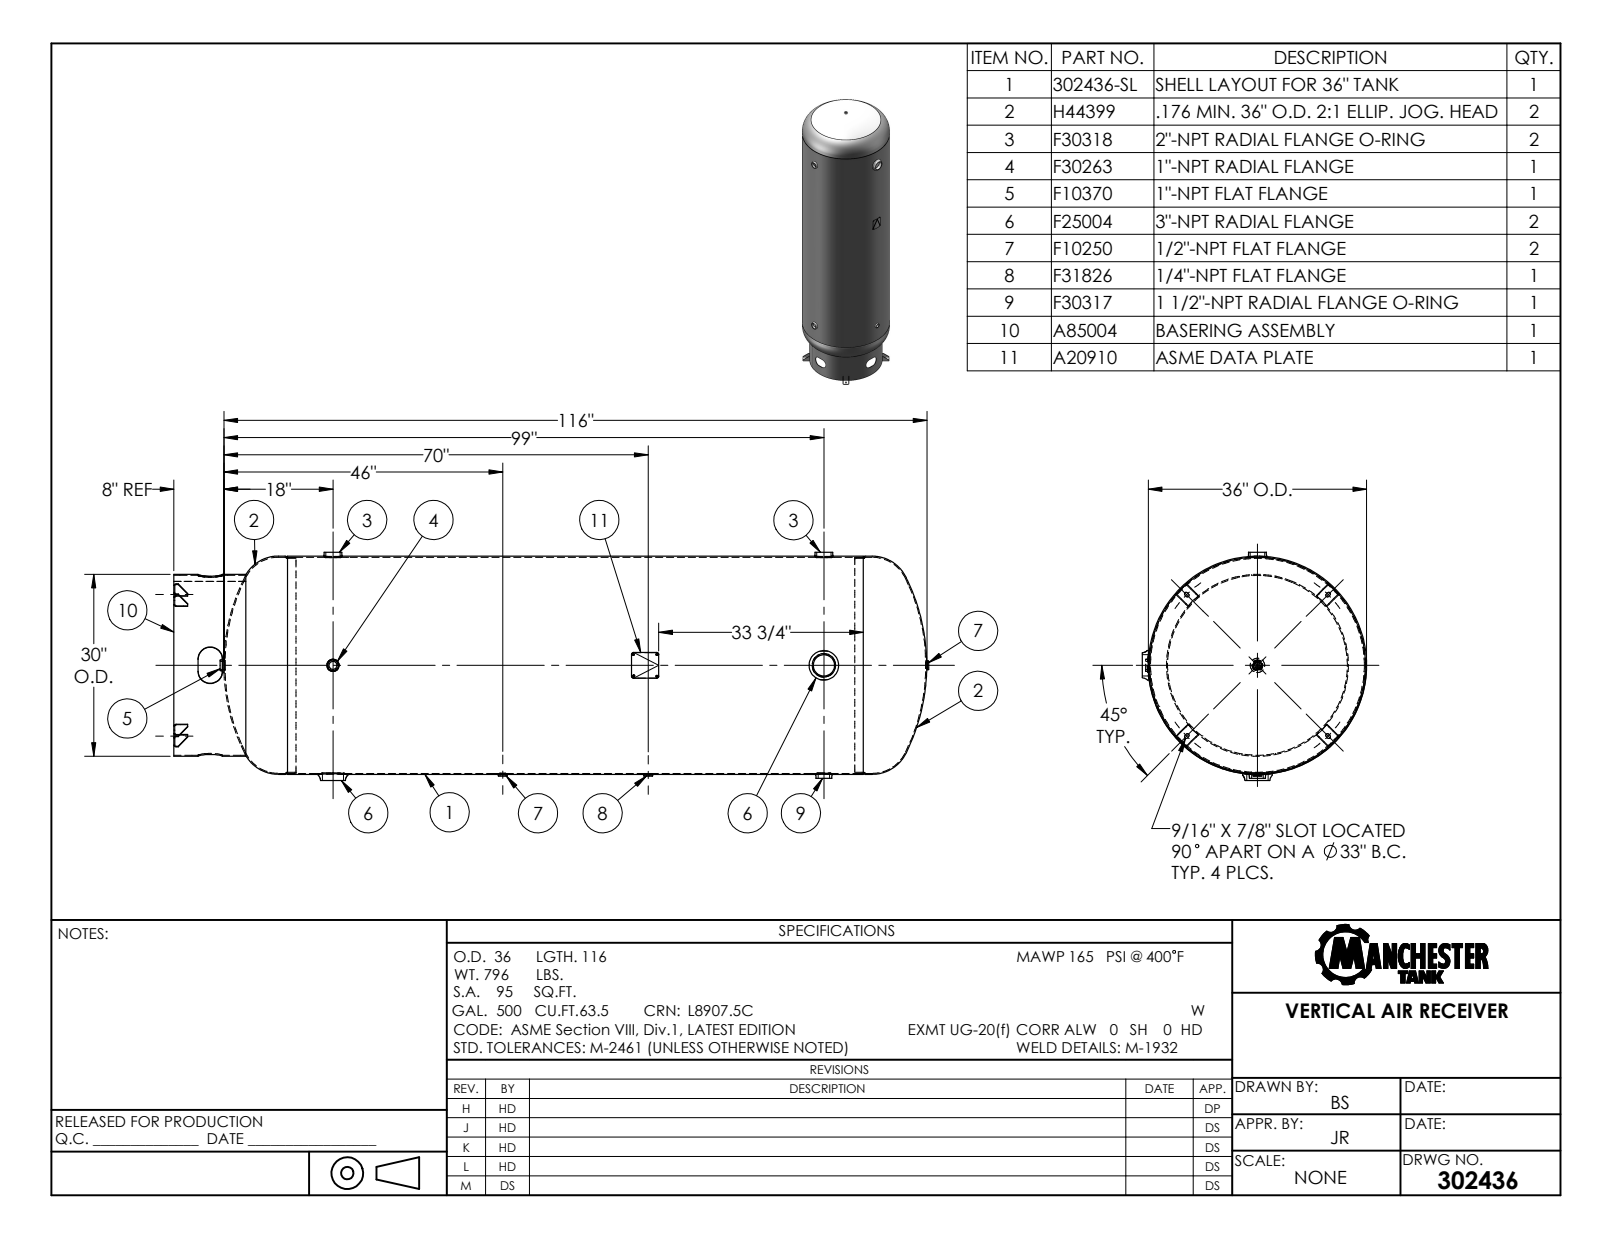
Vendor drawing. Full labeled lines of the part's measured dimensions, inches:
Part name (STEP PRODUCT): 302436
STEP written by: SolidWorks 2011 (CONFIG_CONTROL_DESIGN)
Units: inches
Bodies: 0 solids, 290 faces (94 planar, 94 cylindrical, 102 other)
Overall size (bounding box): 124.78 × 37.822 × 37
Round holes (diameter × count): ⌀0.84 ×2, ⌀3.5 ×2, ⌀0.54 ×1, ⌀1.315 ×1, ⌀1.315 ×1, ⌀1.9 ×1, ⌀2.375 ×1, ⌀2.375 ×1, ⌀29.546 ×1, ⌀35.658 ×1
Round bosses / shafts (diameter × count): ⌀4.25 ×2, ⌀3.625 ×2, ⌀2.375 ×2, ⌀1.813 ×2, ⌀1.188 ×2, ⌀36 ×1, ⌀35.62 ×1, ⌀30 ×1
Partial cylindrical surfaces — rounded edges, fillets, slot ends (radius × count): R0.25 ×8, R0.384 ×8, R0.281 ×6, R18.06 ×1
Main face-to-face distances: 0.134, 0.063, 2.446, 11.875, 101.936, 113.811, 23.75, 78.186, 90.061, 95
Hole centre spacings: 81, 24, 28, 29, 52, 53
